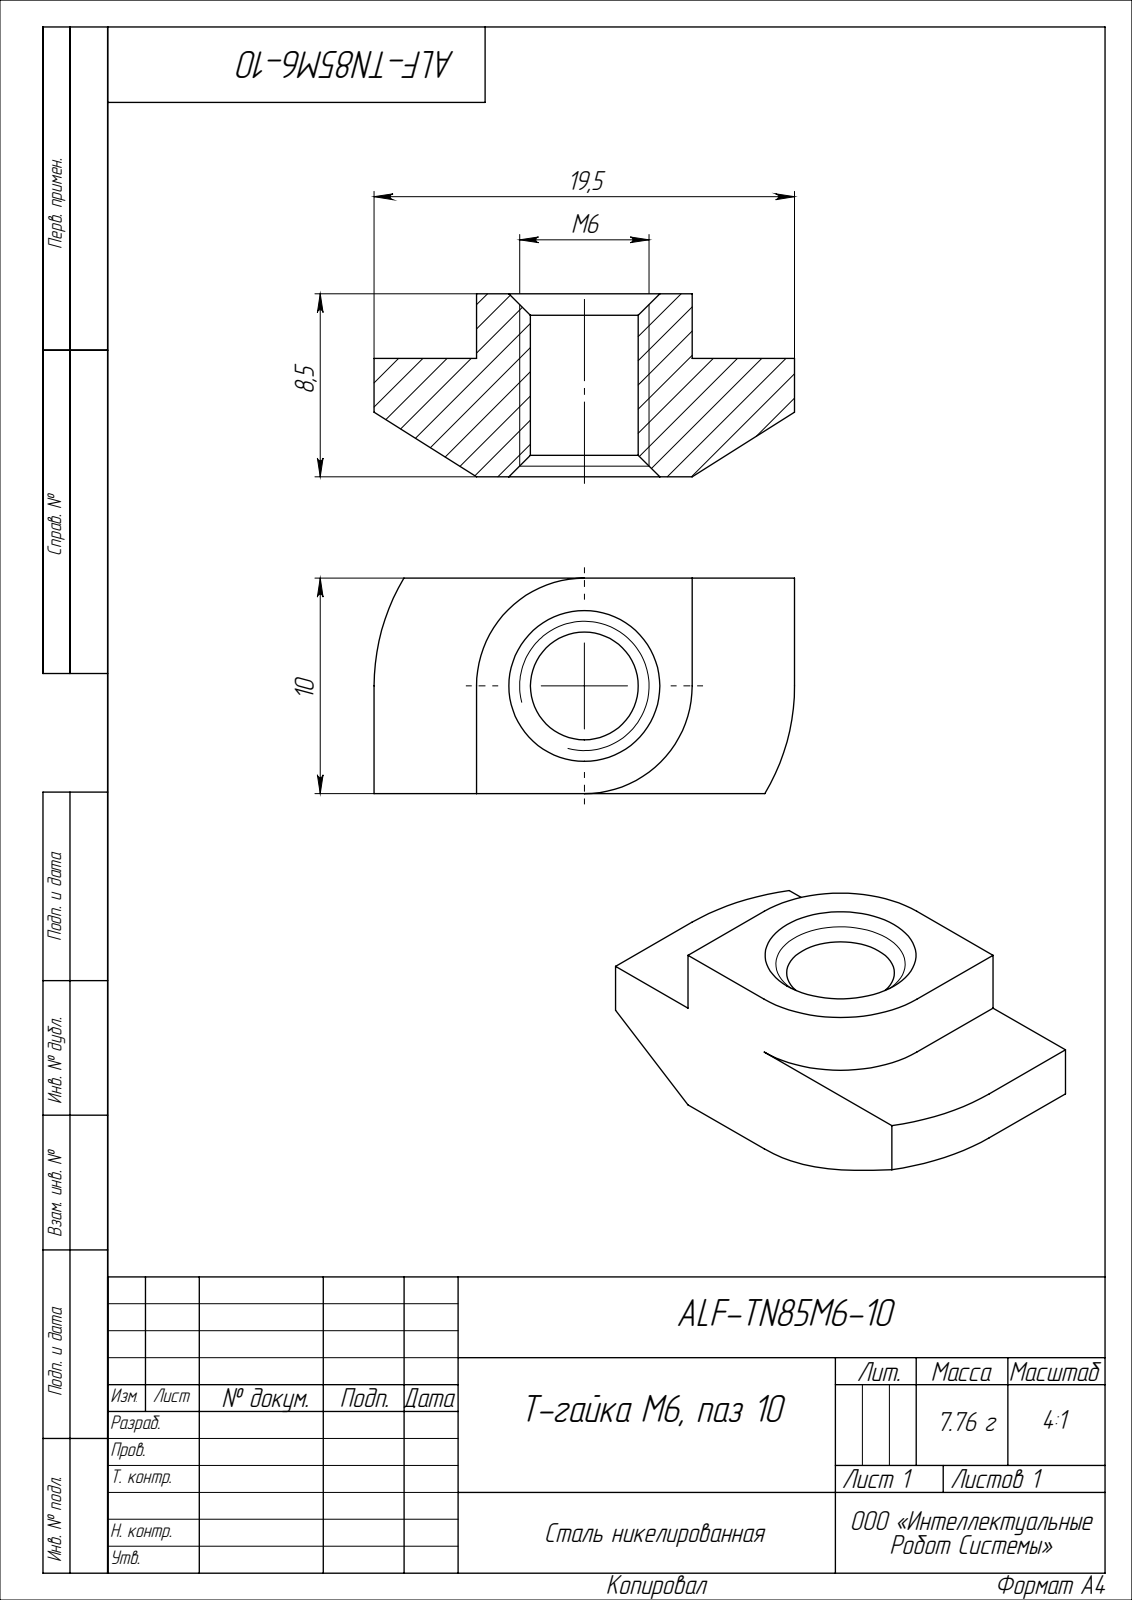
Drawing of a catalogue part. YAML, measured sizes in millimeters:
part_name: "ALF-TN85M6-10"
step_written_by: "SolidWorks 2022 (CONFIG_CONTROL_DESIGN)"
units: millimeters
bodies: {solids: 1, faces: 24, planar: 12, cylindrical: 6, other: 6}
overall_size: [19.5, 10, 8.5]
volume: 982
surface_area: 802
round_holes:
  - {diameter: 5, count: 1}
partial_cylinders:
  - {radius: 5, count: 1}
  - {radius: 9.75, count: 1}
face_to_face_distances: [10, 5.5, 8.5, 3, 4.75, 14.75, 19.5]
